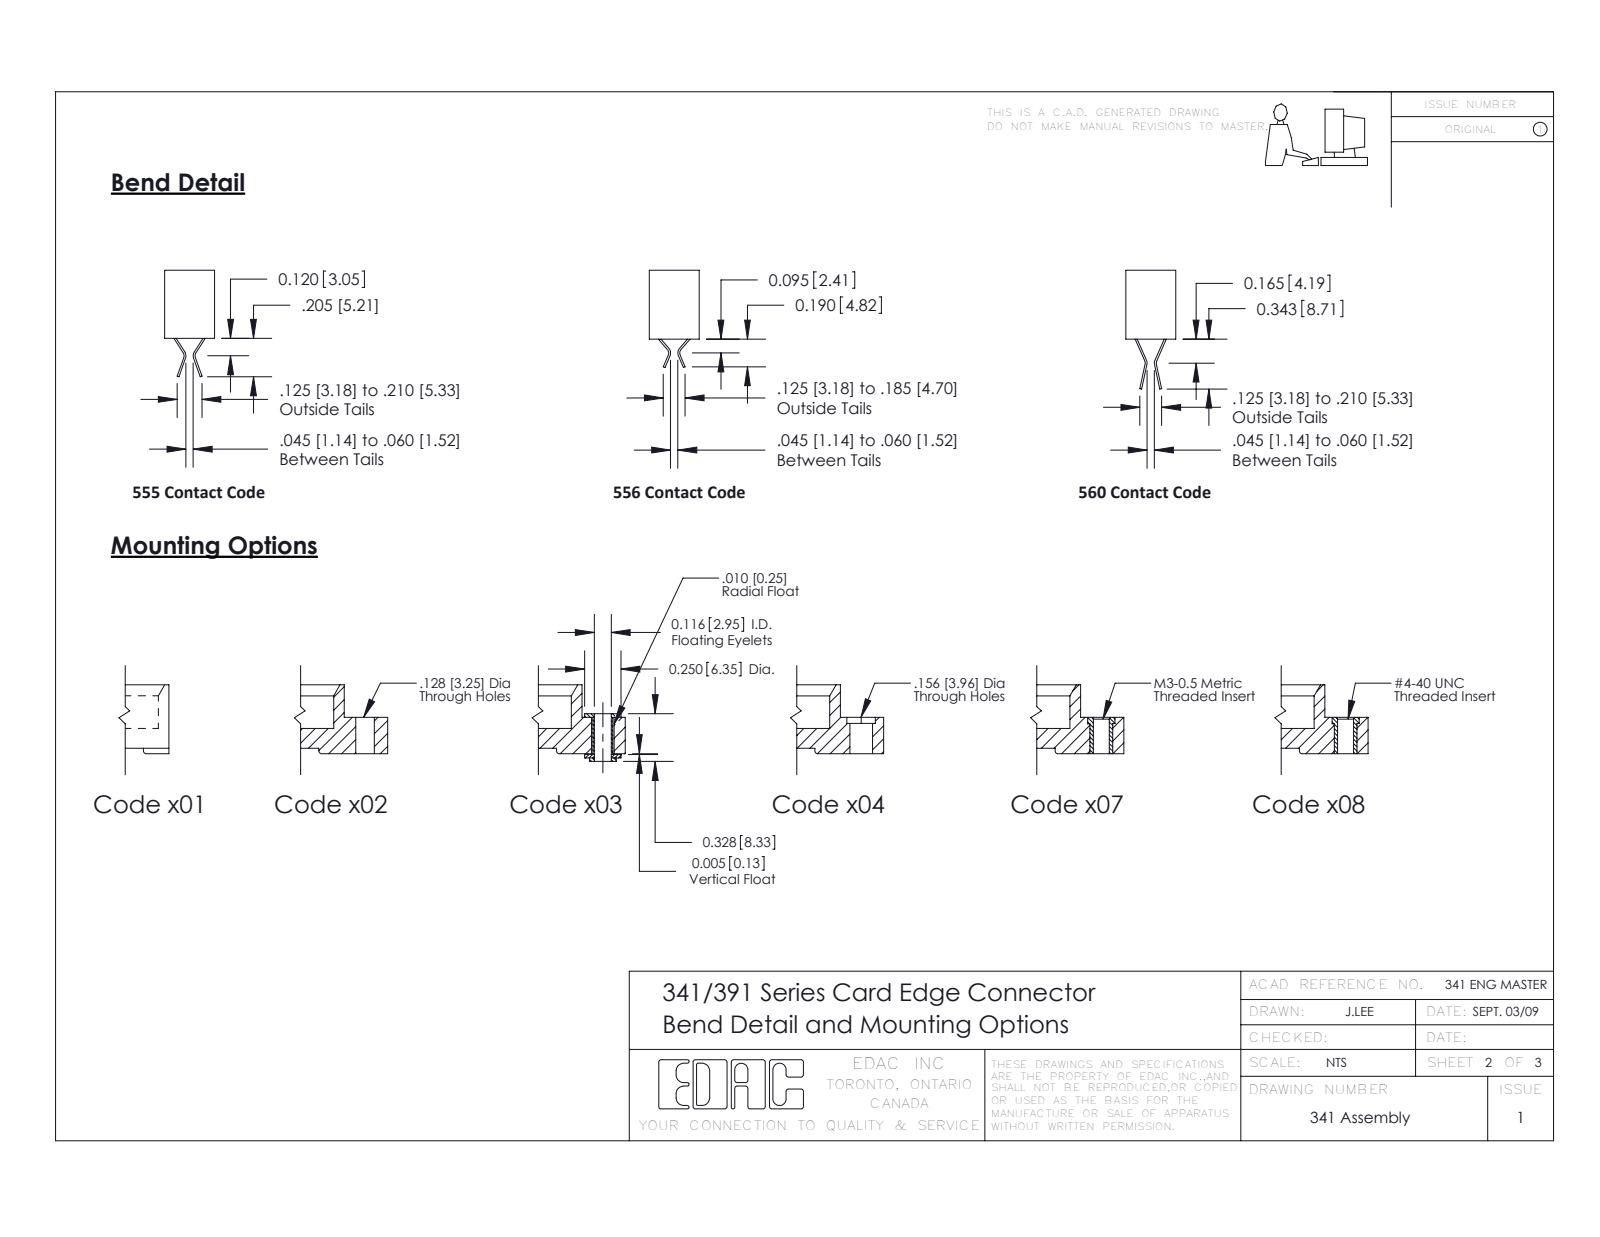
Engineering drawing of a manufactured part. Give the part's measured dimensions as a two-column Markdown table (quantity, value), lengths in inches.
| quantity | value |
| --- | --- |
| part name | 341-010-524-102; 341-292-001_341-292-124; 341 Part_.128 (3.25) Dia Mounting Holes |
| STEP written by | SolidWorks 2016 (CONFIG_CONTROL_DESIGN) |
| units | inches |
| bodies | 11 solids, 936 faces (578 planar, 318 cylindrical, 40 other) |
| overall size | 1.875 × 0.537 × 0.33 |
| volume | 0.161 in³ |
| surface area | 6.213 in² |
| round holes (diameter × count) | 0.128 × 2 |
| partial cylindrical surfaces (radius × count) | 0.015 × 62, 0.01 × 22, 0.02 × 21, 0.004 × 20, 0.013 × 10, 0.007 × 6, 0.031 × 6, 0.026 × 3 |
| main face-to-face distances | 0.1, 0.3, 0.2, 0.33, 0.4, 0.041, 0.289, 0.144, 0.5, 0.056 |
| hole center spacings | 1.575 |
